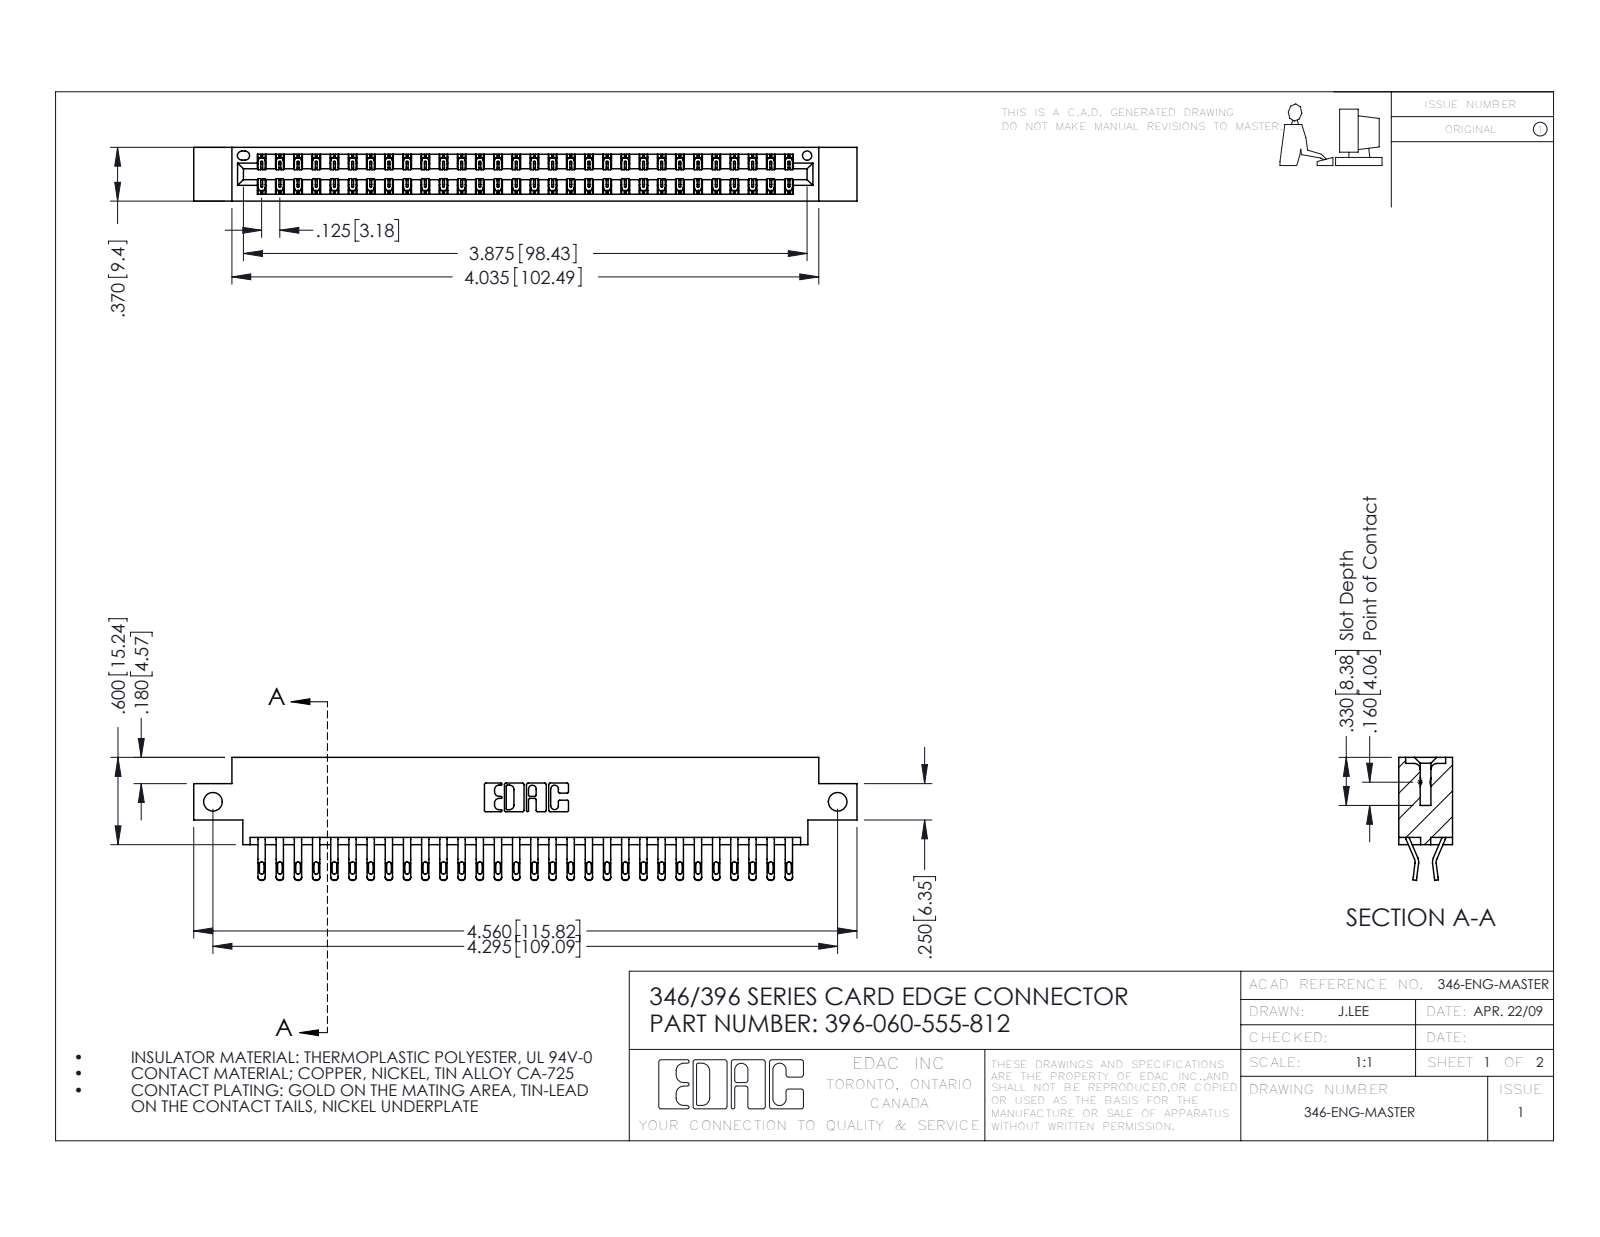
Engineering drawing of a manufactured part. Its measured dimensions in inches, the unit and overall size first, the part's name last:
Units: inches
Overall size (bounding box): 4.56 × 0.845 × 0.37
Round holes (diameter × count): ⌀0.128 ×2, ⌀0.064 ×1
Partial cylindrical surfaces — rounded edges, fillets, slot ends (radius × count): R0.016 ×120, R0.02 ×120, R0.006 ×90, R0.01 ×22, R0.007 ×6, R0.031 ×6, R0.026 ×3, R0.01 ×2
Main face-to-face distances: 0.048, 0.322, 0.37, 0.25, 0.025, 0.072, 0.298, 0.275, 0.148, 0.222
Hole centre spacings: 4.295
Volume: 0.679 in³ · Surface area: 24.45 in²
Bodies: 61 solids, 3606 faces (2060 planar, 1546 cylindrical, 0 other)
Part name (STEP PRODUCT): 346 Part_0.170 Offset - Side Mount; 396-060-555-812; 345-292-001_555 Tail
STEP written by: SolidWorks 2016 (CONFIG_CONTROL_DESIGN)
